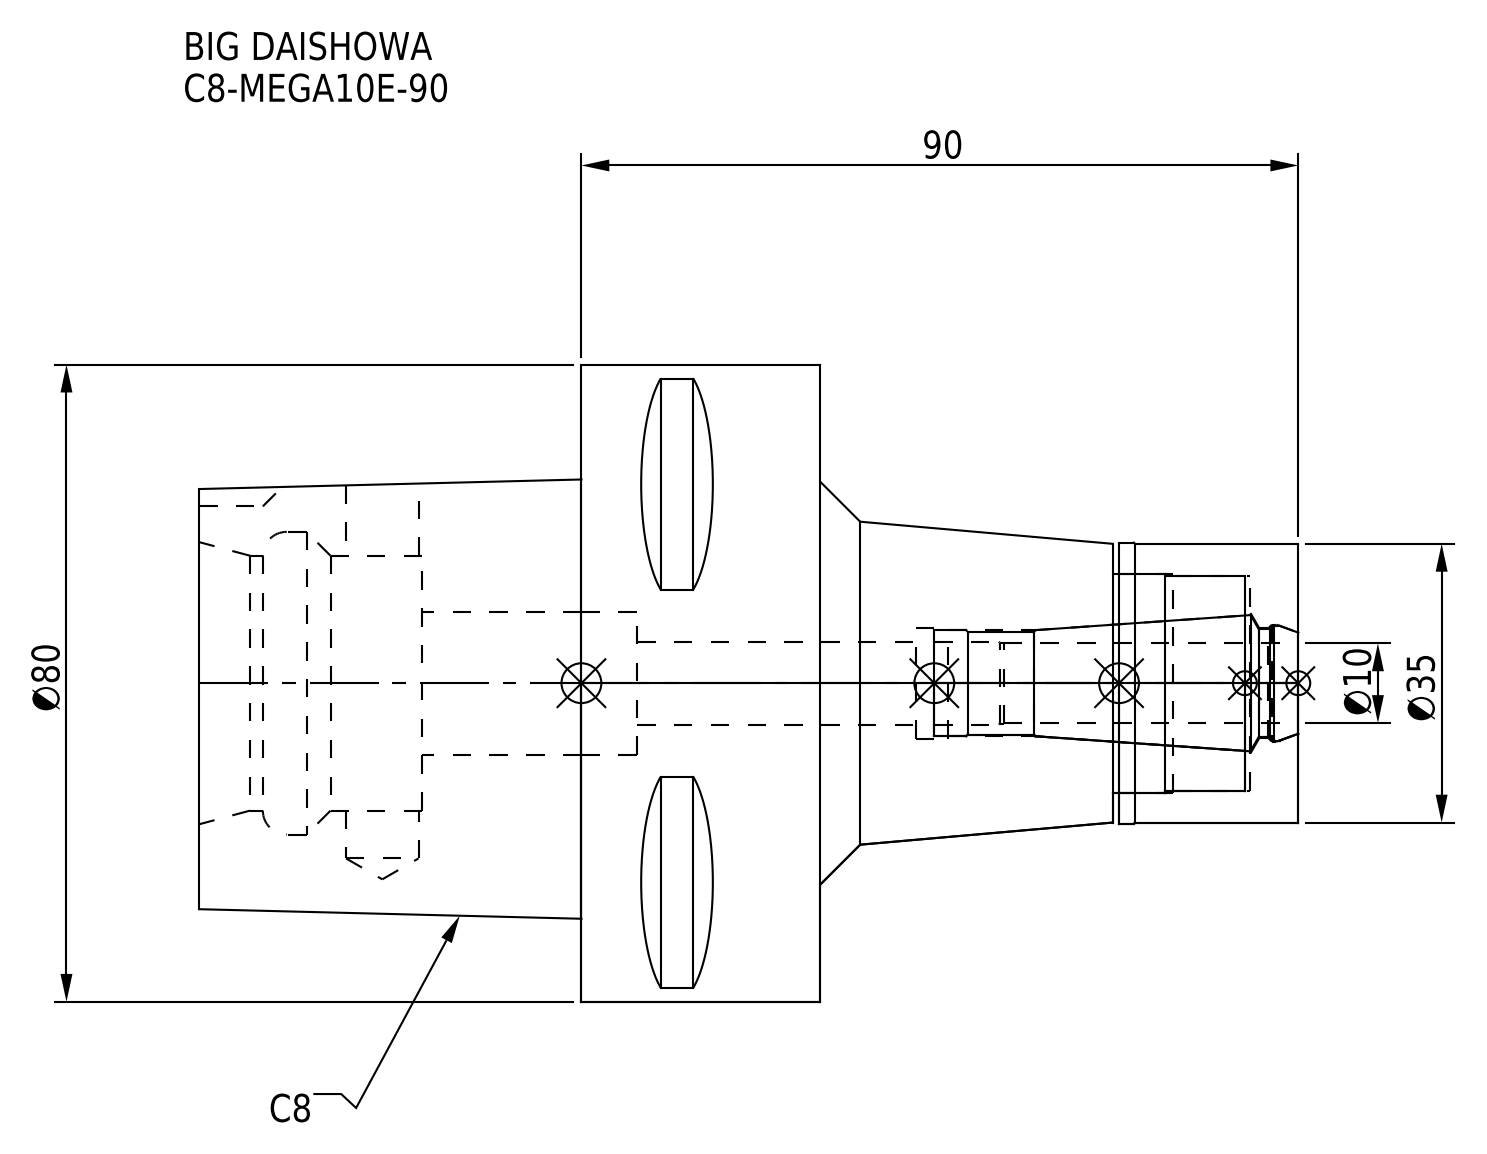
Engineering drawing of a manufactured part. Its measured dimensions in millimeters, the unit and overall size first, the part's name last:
Units: millimetres
Overall size (bounding box): 138 × 80 × 80
Round holes (diameter × count): ⌀9.1 ×1, ⌀10.4 ×1, ⌀13.3 ×1, ⌀13.8 ×1, ⌀13.9 ×1, ⌀14.7 ×1, ⌀18 ×1, ⌀27 ×1, ⌀27.5 ×1, ⌀32 ×1, ⌀38 ×1
Round bosses / shafts (diameter × count): ⌀80 ×1, ⌀35.3 ×1, ⌀35 ×1
Partial cylindrical surfaces — rounded edges, fillets, slot ends (radius × count): R6 ×1
Main face-to-face distances: 30, 48, 78, 90, 60, 138, 20, 110, 50, 28
Volume: 277 828 mm³ · Surface area: 44 797 mm²
Bodies: 2 solids, 97 faces (36 planar, 37 cylindrical, 24 other)
Part name (STEP PRODUCT): C8-MEGA10E-90_1.stp; MEN10_1.stp; C8-MEGA10E-90-100.stp; C8-MEGA10E-90 (+3 more)
STEP written by: SolidWorks 2019 (CONFIG_CONTROL_DESIGN)
